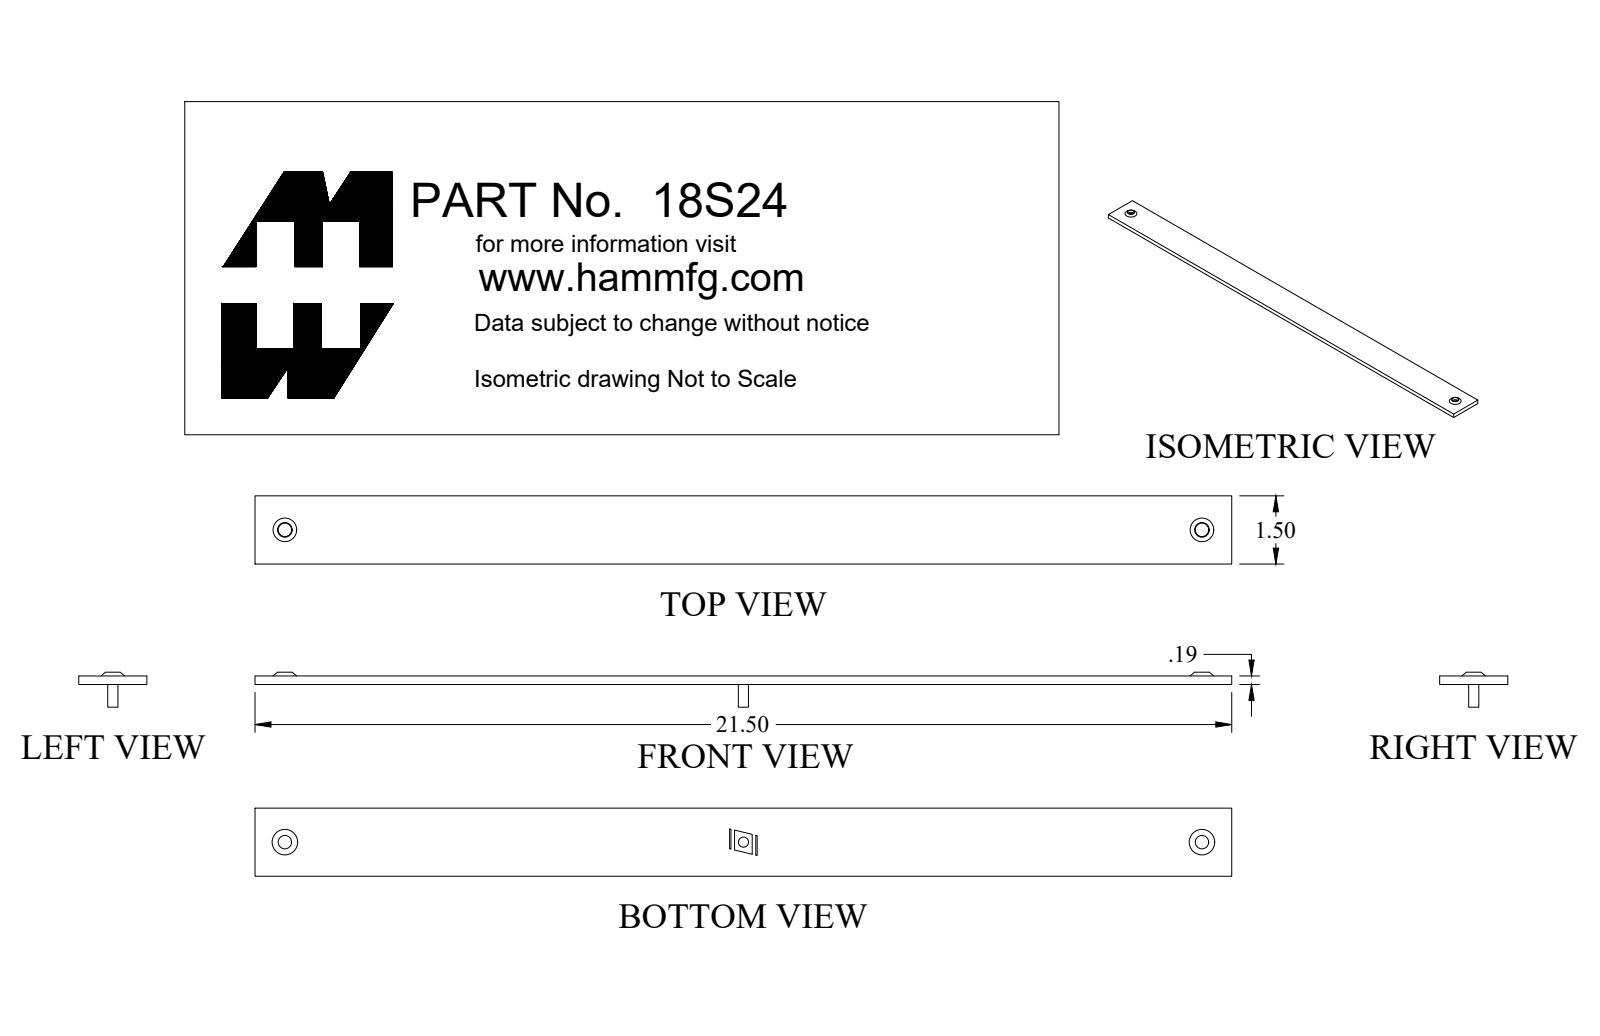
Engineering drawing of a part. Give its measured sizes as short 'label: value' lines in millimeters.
name: 18S24_Default
written by: SolidWorks 2018 (CONFIG_CONTROL_DESIGN)
unit: mm
bodies: 1 solid, 20 faces (8 planar, 4 cylindrical, 8 other)
size: 546.1 × 38.1 × 6.9
volume: 98 730 mm³; area: 47 330 mm²
holes: 2× ⌀7.5
face distances: 4.8, 38.1, 546.1, 6.9, 2.1
hole spacings: 512.8
